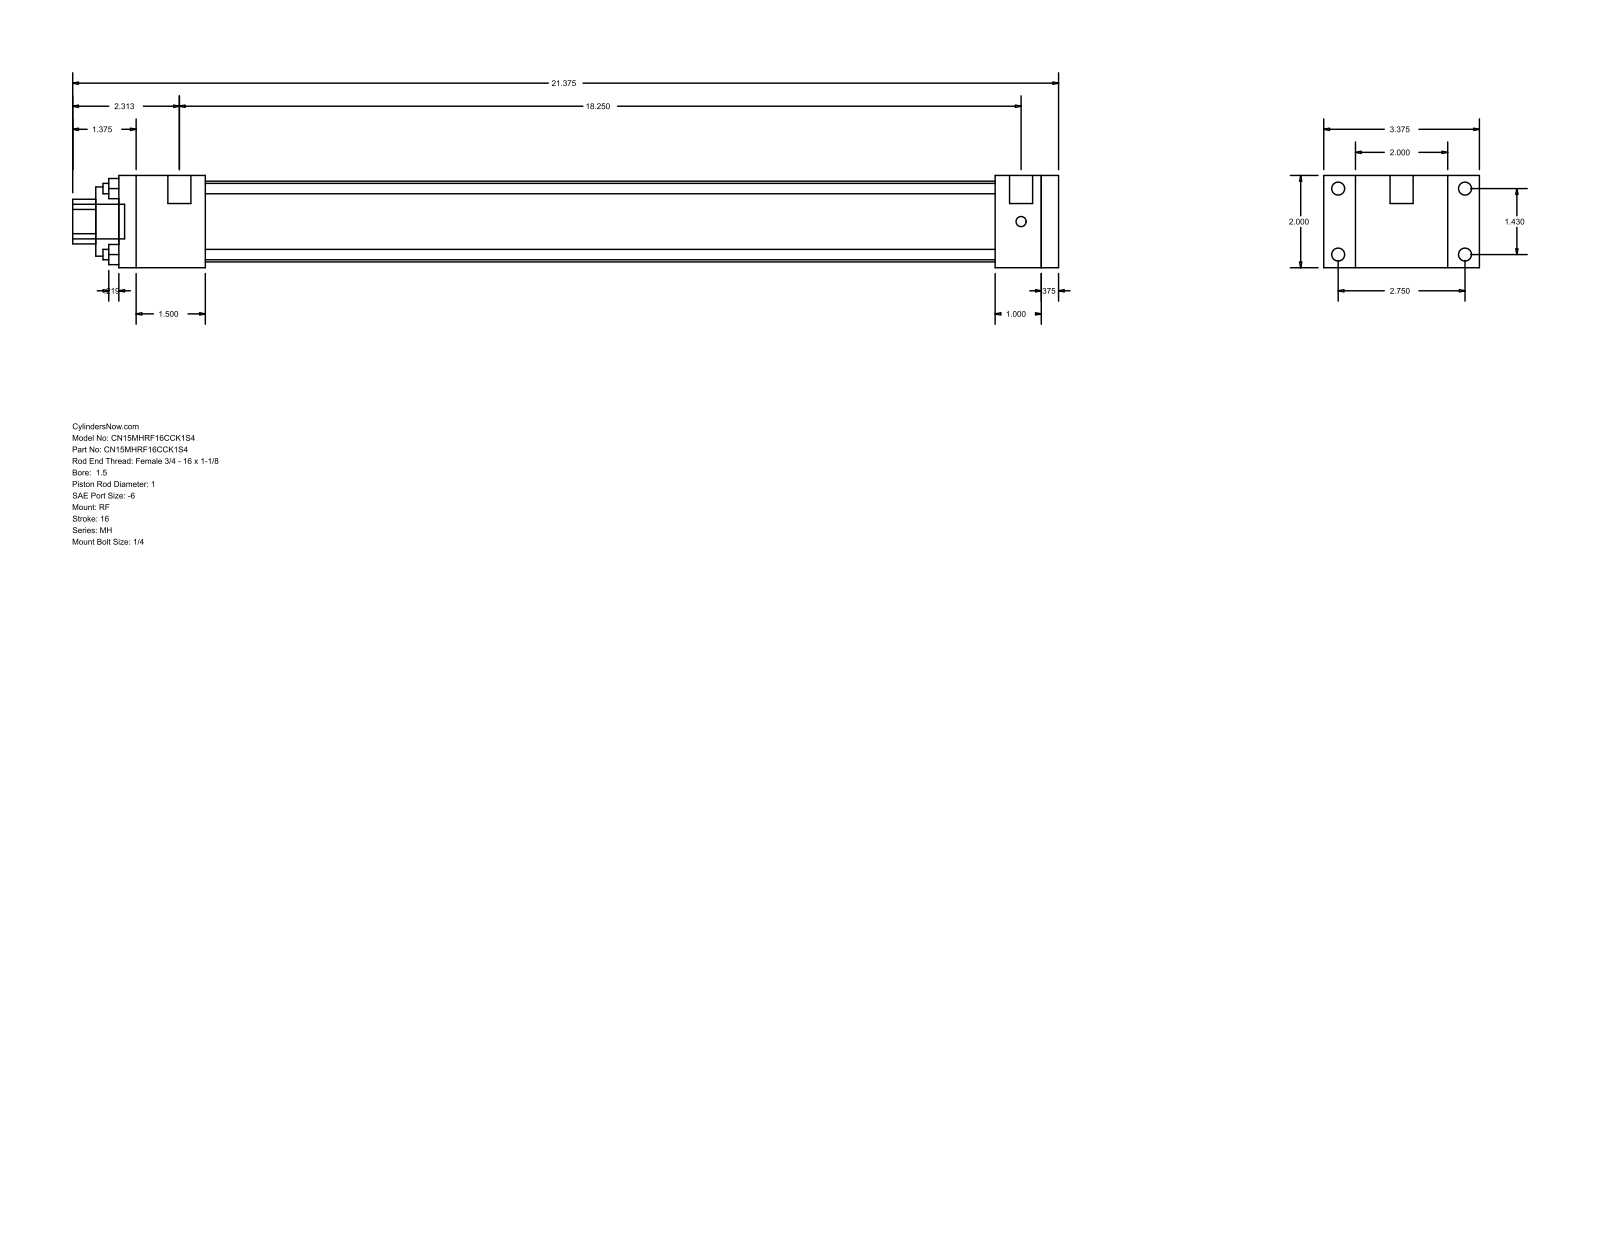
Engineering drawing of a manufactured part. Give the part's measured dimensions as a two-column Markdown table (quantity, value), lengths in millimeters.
| quantity | value |
| --- | --- |
| part name | MH_RF__0150_1 |
| STEP written by | GSSL Pune (CONFIG_CONTROL_DESIGN) |
| units | millimeters |
| bodies | 0 solids, 92 faces (64 planar, 28 cylindrical, 0 other) |
| overall size | 542.92 × 85.72 × 50.8 |
| round holes (diameter × count) | 5.71 × 4, 25.4 × 1, 38.1 × 1, 44.45 × 1 |
| round bosses / shafts (diameter × count) | 7.14 × 4, 5.56 × 4, 12.7 × 2, 19.05 × 1 |
| partial cylindrical surfaces (radius × count) | 12.29 × 1 |
| main face-to-face distances | 50.8, 9.52, 508, 25.4, 517.52, 17.46, 68.26, 482.6, 34.92, 47.63 |
| hole center spacings | 25.68, 36.32, 51.36 |
